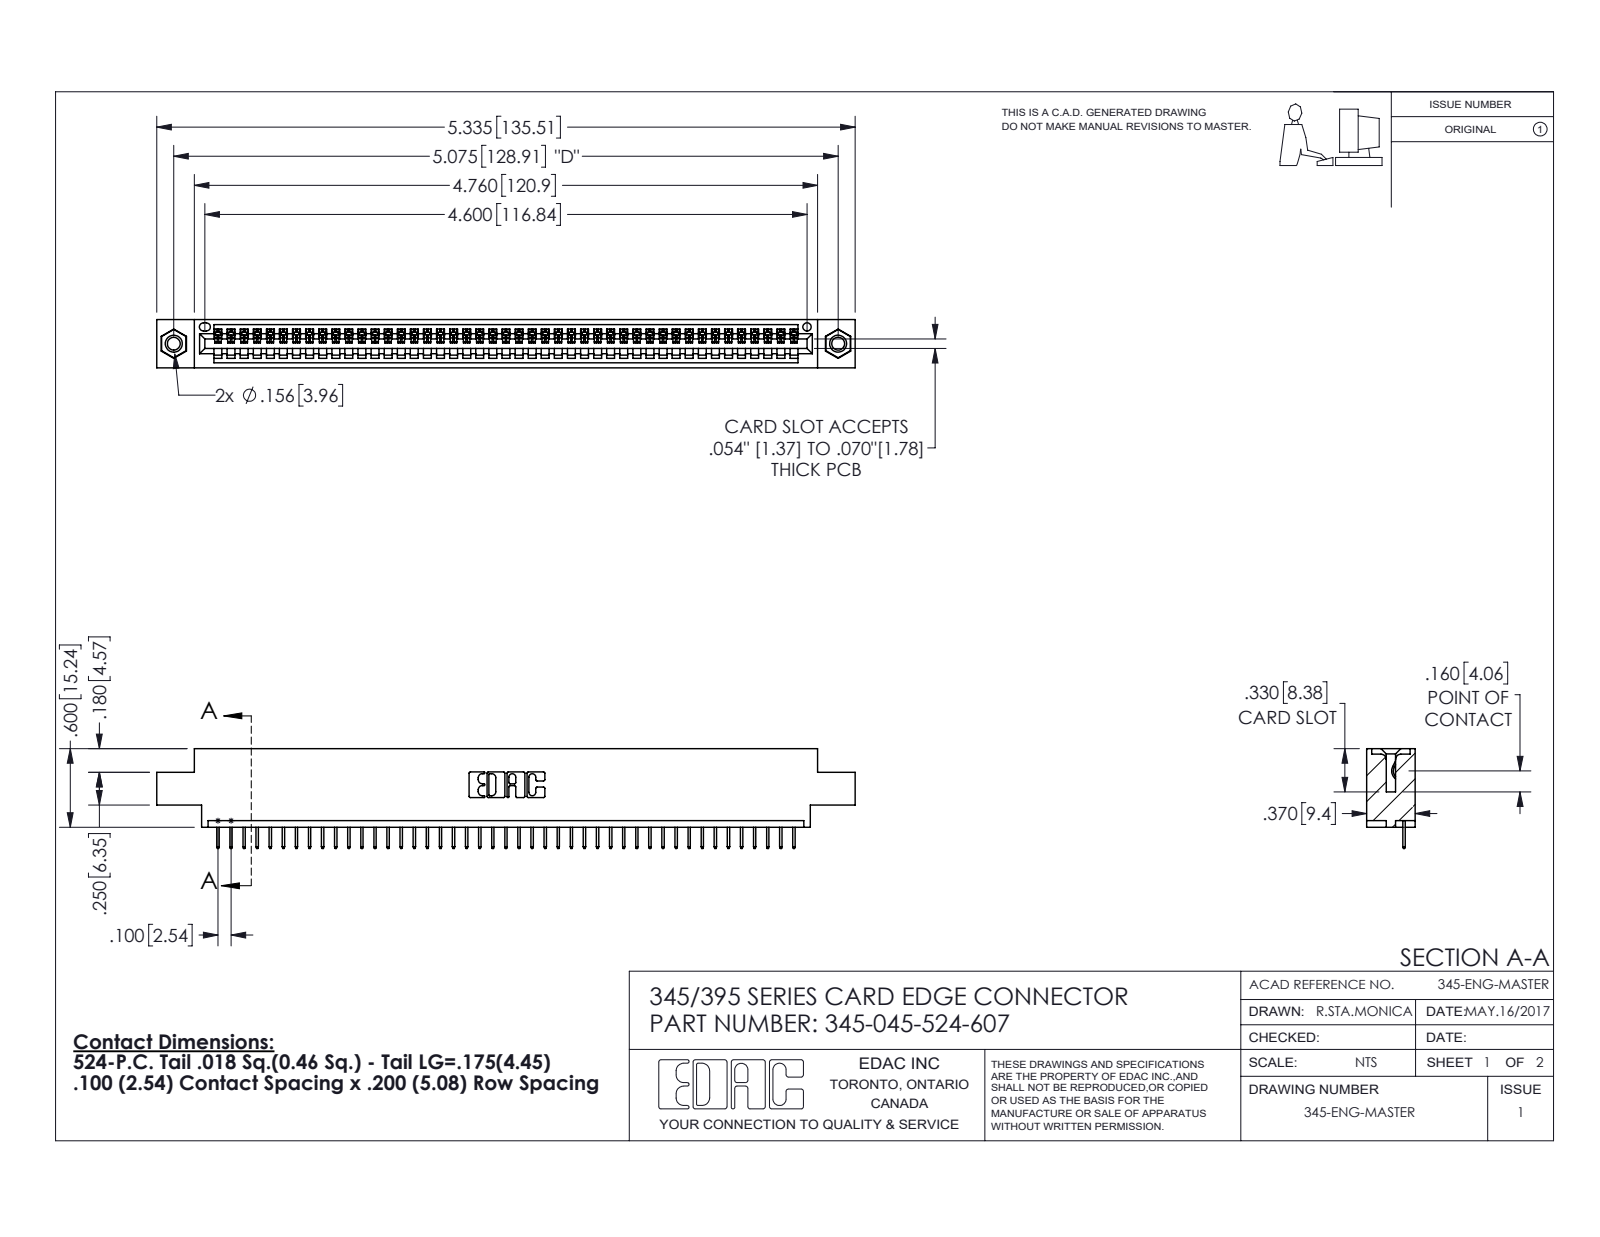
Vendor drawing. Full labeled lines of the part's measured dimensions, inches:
Part name (STEP PRODUCT): 345-292-001_345-293-124; 345 Part_0.170 Offset - 0.156 Dia-TI; 345-045-524-607; 345-250-001_345-250-005-103
STEP written by: SolidWorks 2016 (CONFIG_CONTROL_DESIGN)
Units: inches
Bodies: 48 solids, 2980 faces (2186 planar, 778 cylindrical, 16 other)
Overall size (bounding box): 5.335 × 0.762 × 0.37
Volume: 0.768 in³ · Surface area: 25.36 in²
Round holes (diameter × count): ⌀0.098 ×2, ⌀0.125 ×2, ⌀0.156 ×2, ⌀0.064 ×1
Round bosses / shafts (diameter × count): ⌀0.155 ×2
Partial cylindrical surfaces — rounded edges, fillets, slot ends (radius × count): R0.006 ×90, R0.01 ×22, R0.007 ×6, R0.031 ×6, R0.026 ×3, R0.031 ×2, R0.04 ×2, R0.014 ×1
Main face-to-face distances: 0.072, 0.298, 0.37, 0.2, 0.098, 0.272, 0.025, 0.225, 0.072, 0.175
Hole centre spacings: 0.27, 4.839, 5.075
